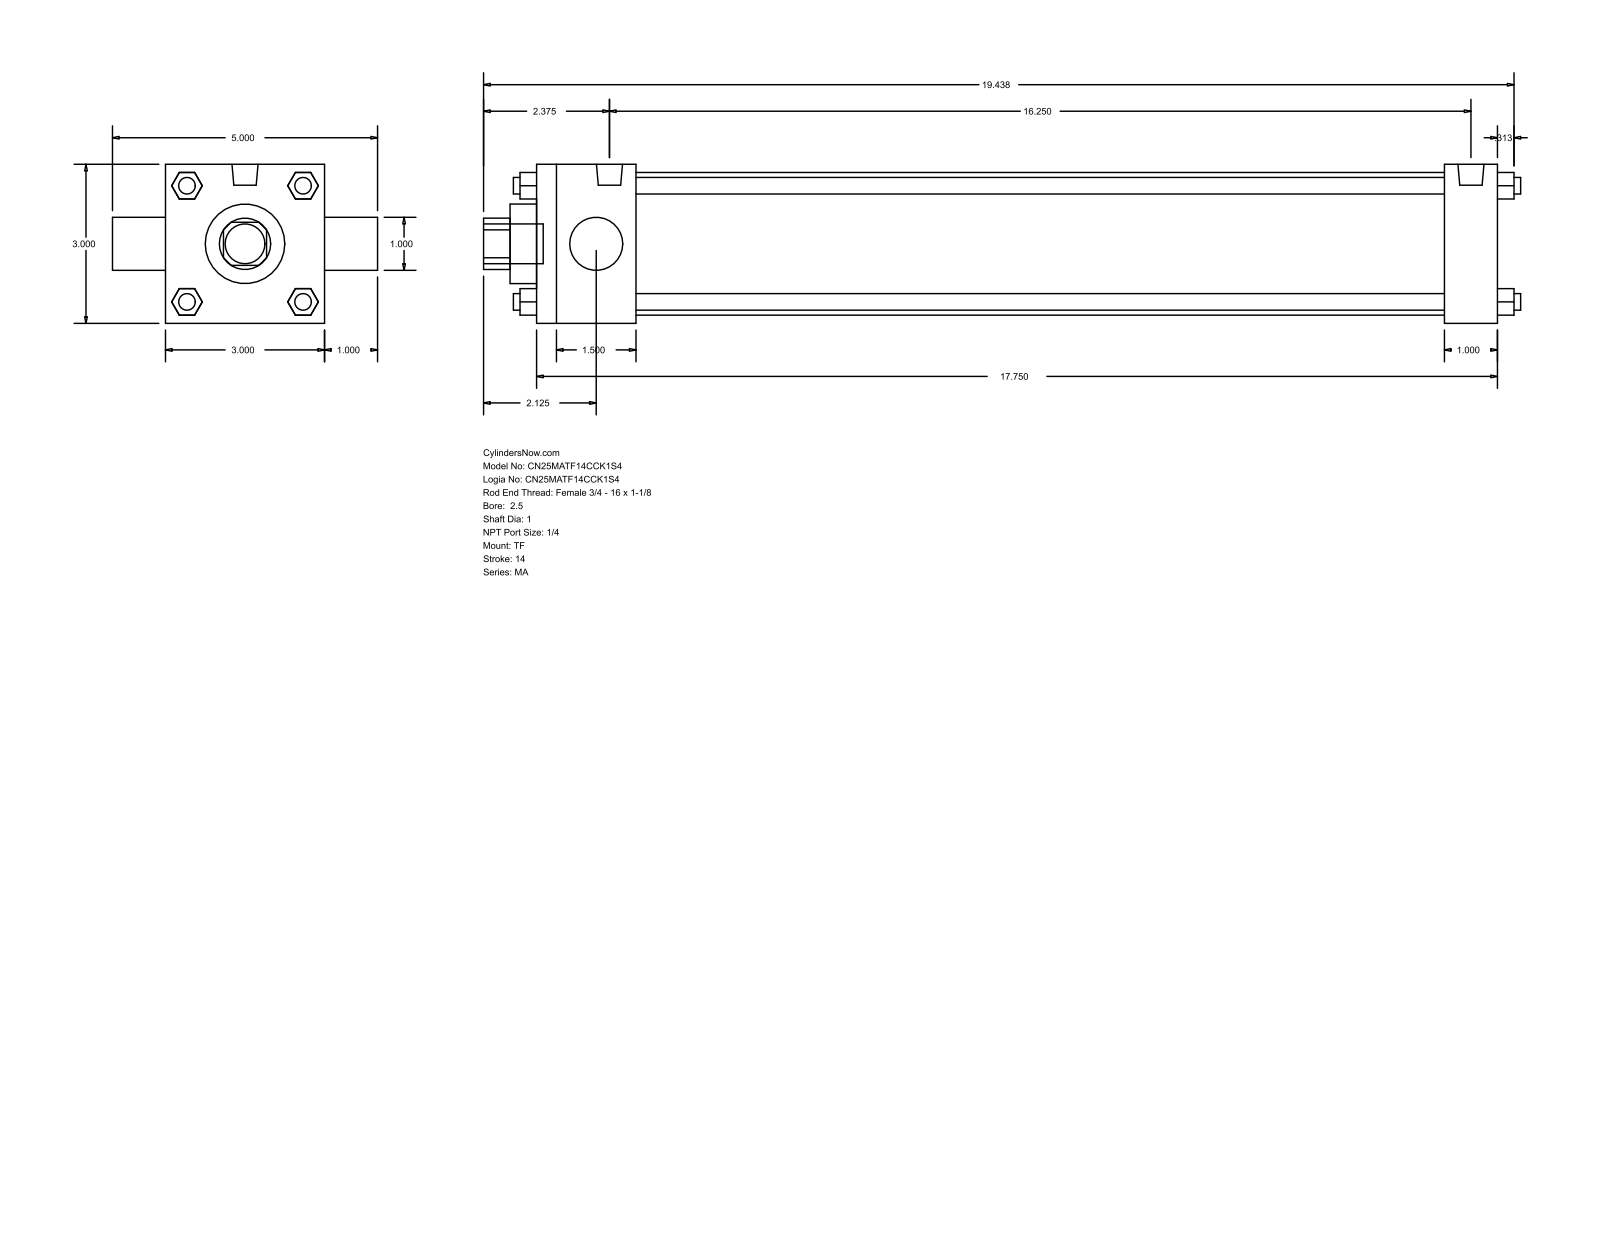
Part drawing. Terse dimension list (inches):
name: MA_TF__0250_1
written by: GSSL Pune (CONFIG_CONTROL_DESIGN)
unit: in
bodies: 0 solids, 120 faces (92 planar, 28 cylindrical, 0 other)
size: 19.563 × 5 × 3
holes: 2× ⌀1, 1× ⌀1.5, 1× ⌀2.69
bosses: 7× ⌀0.313, 2× ⌀0.492, 1× ⌀0.75
rounds: 1× R0.484
face distances: 3, 18.125, 0.5, 1.875, 17.125, 15.25, 16.25, 1, 1, 4
